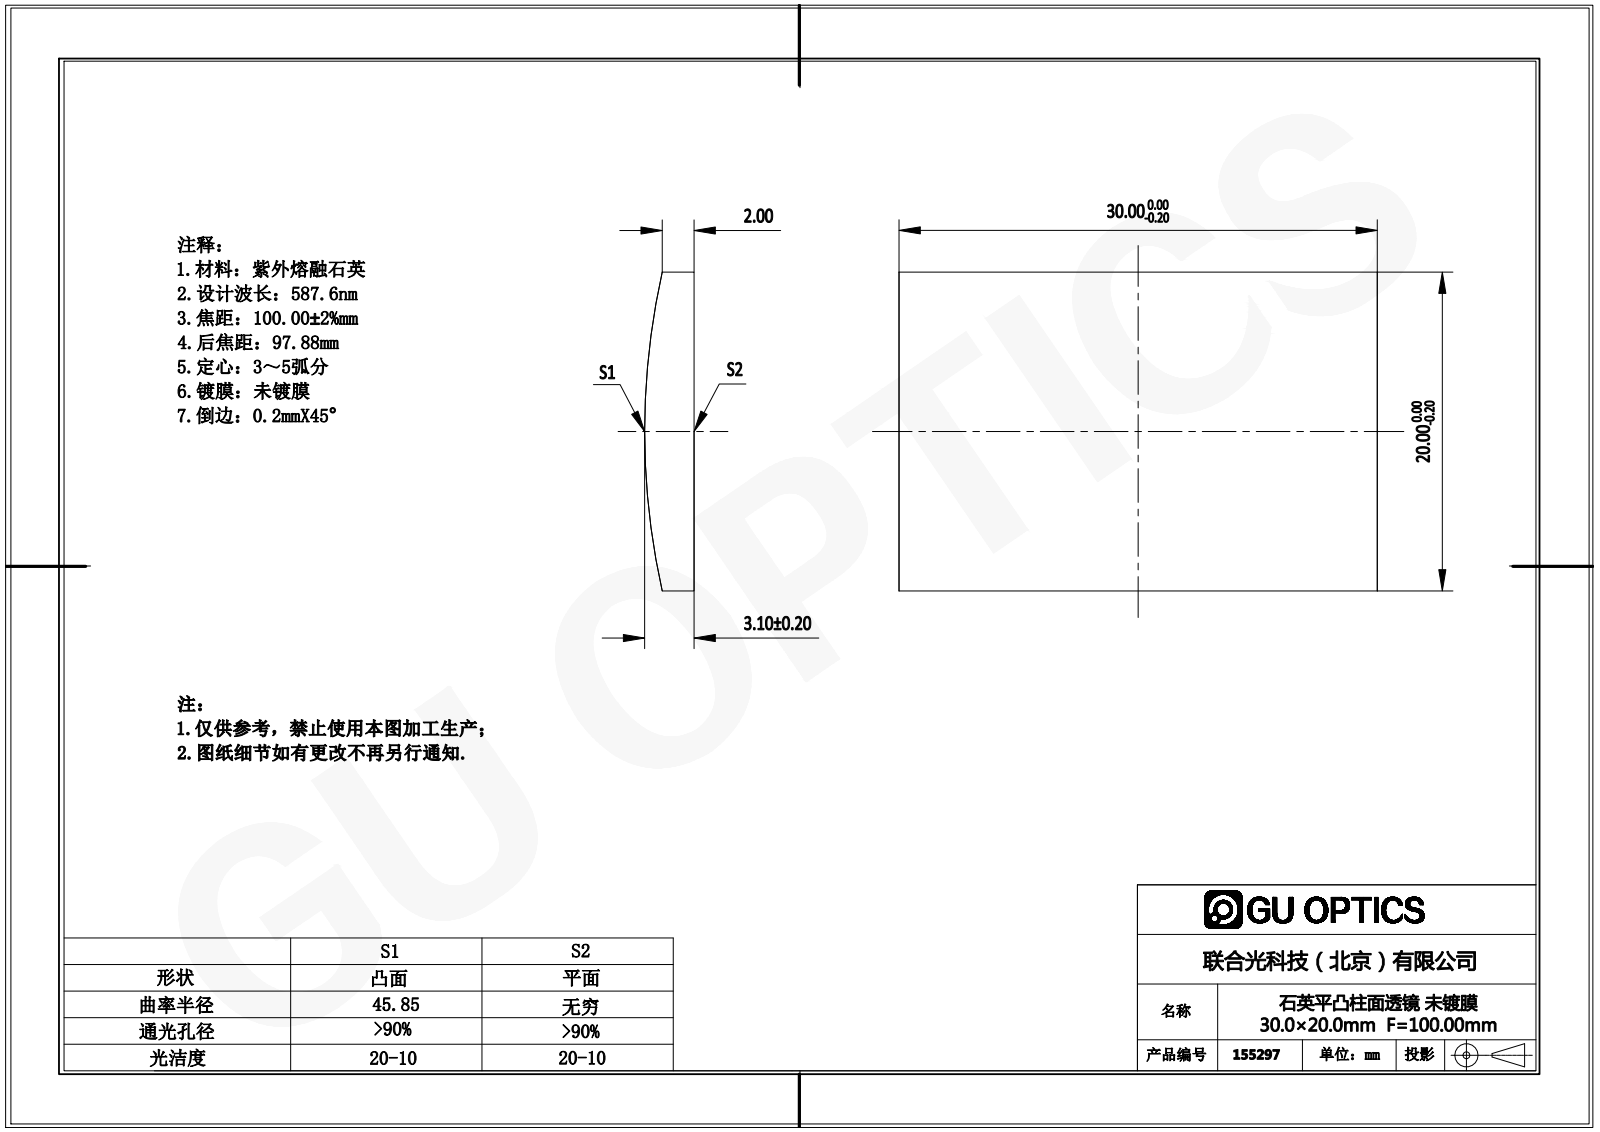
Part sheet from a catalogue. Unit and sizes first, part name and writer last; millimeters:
Units: millimetres
Overall size (bounding box): 30 × 20 × 3.1
Partial cylindrical surfaces — rounded edges, fillets, slot ends (radius × count): R45.85 ×1
Main face-to-face distances: 20, 30
Volume: 1 640 mm³ · Surface area: 1 434 mm²
Bodies: 1 solid, 6 faces (5 planar, 1 cylindrical, 0 other)
Part name (STEP PRODUCT): 155297
STEP written by: SolidWorks 2016 (AUTOMOTIVE_DESIGN)
